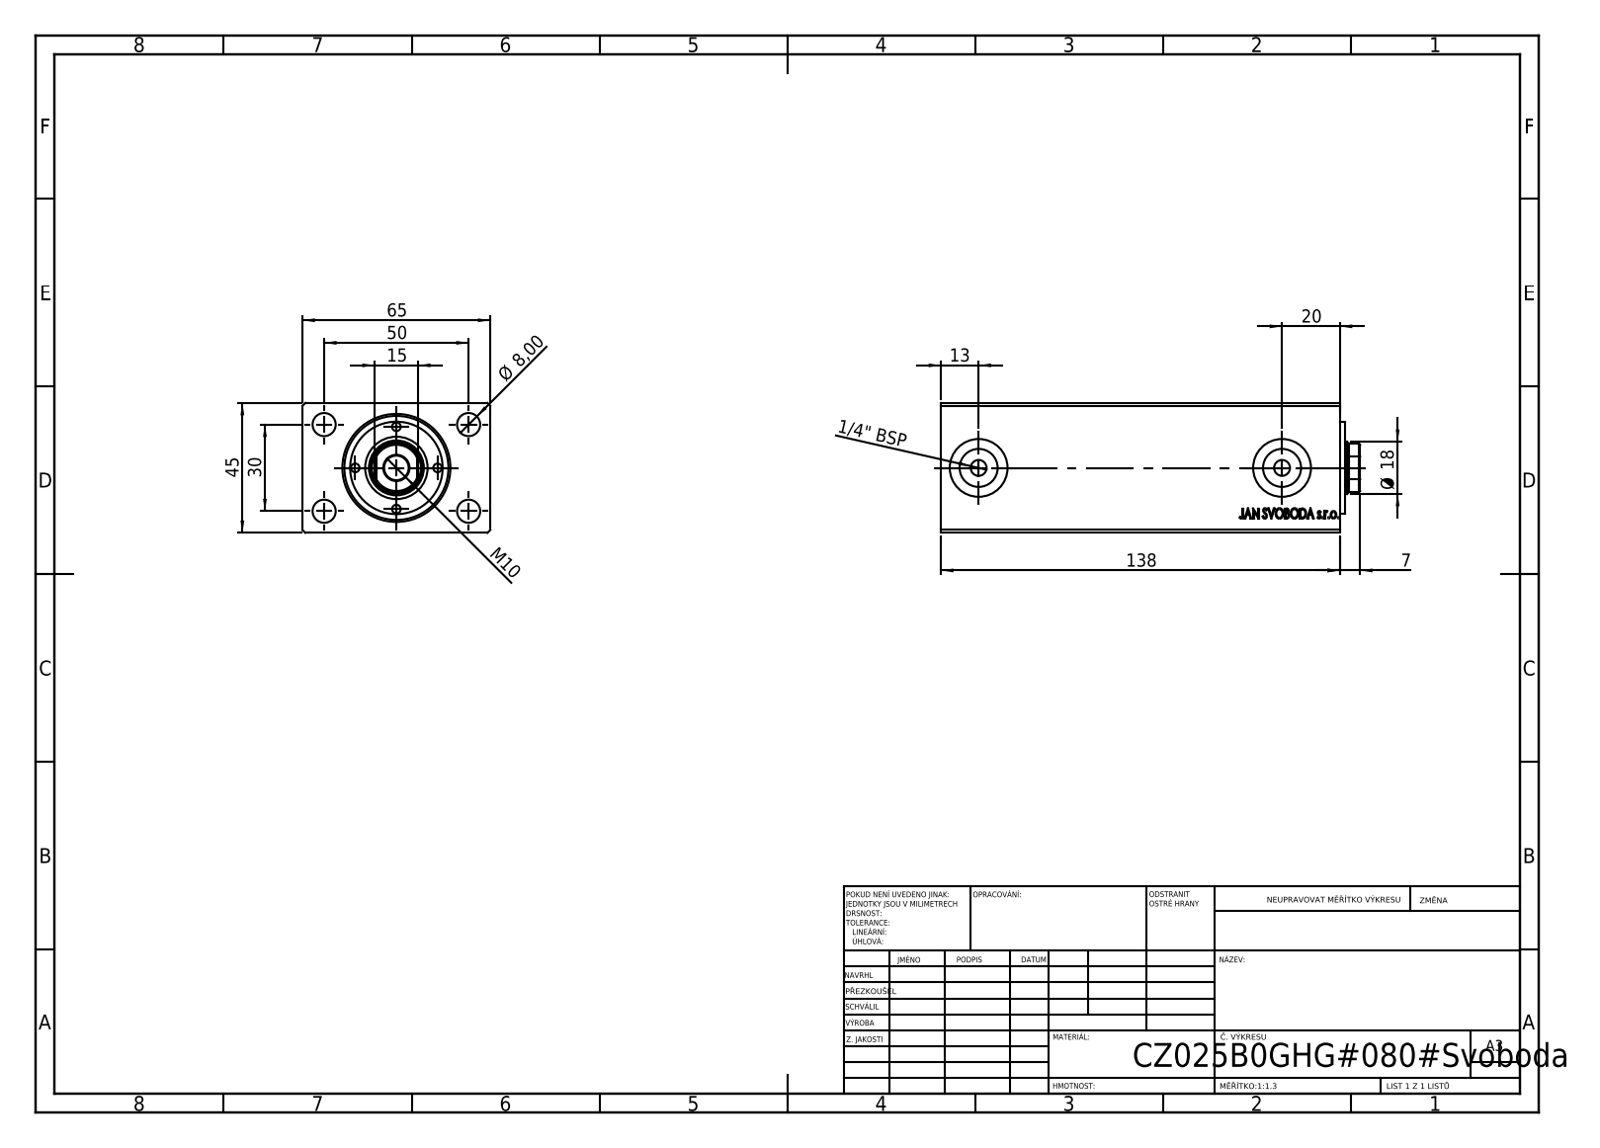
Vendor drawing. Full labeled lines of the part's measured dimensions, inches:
Part name (STEP PRODUCT): V500CZ; V500CZ_B_VC
STEP written by: SolidWorks 2019 (CONFIG_CONTROL_DESIGN)
Units: inches
Bodies: 3 solids, 873 faces (399 planar, 58 cylindrical, 416 other)
Overall size (bounding box): 5.709 × 2.559 × 1.772
Volume: 22.59 in³ · Surface area: 100.3 in²
Round holes (diameter × count): ⌀0.118 ×4, ⌀0.315 ×4, ⌀0.217 ×2, ⌀0.518 ×2, ⌀0.787 ×2, ⌀0.335 ×1, ⌀0.709 ×1, ⌀0.748 ×1, ⌀0.984 ×1, ⌀1.417 ×1
Round bosses / shafts (diameter × count): ⌀1.26 ×1
Partial cylindrical surfaces — rounded edges, fillets, slot ends (radius × count): R0.335 ×1
Main face-to-face distances: 1.772, 2.559, 5.433, 0.276, 5.425, 4.929, 0.496, 0.504, 0.071, 0.205
Hole centre spacings: 0.561, 0.726, 0.793, 0.985, 1.148, 1.515, 1.654, 1.122
